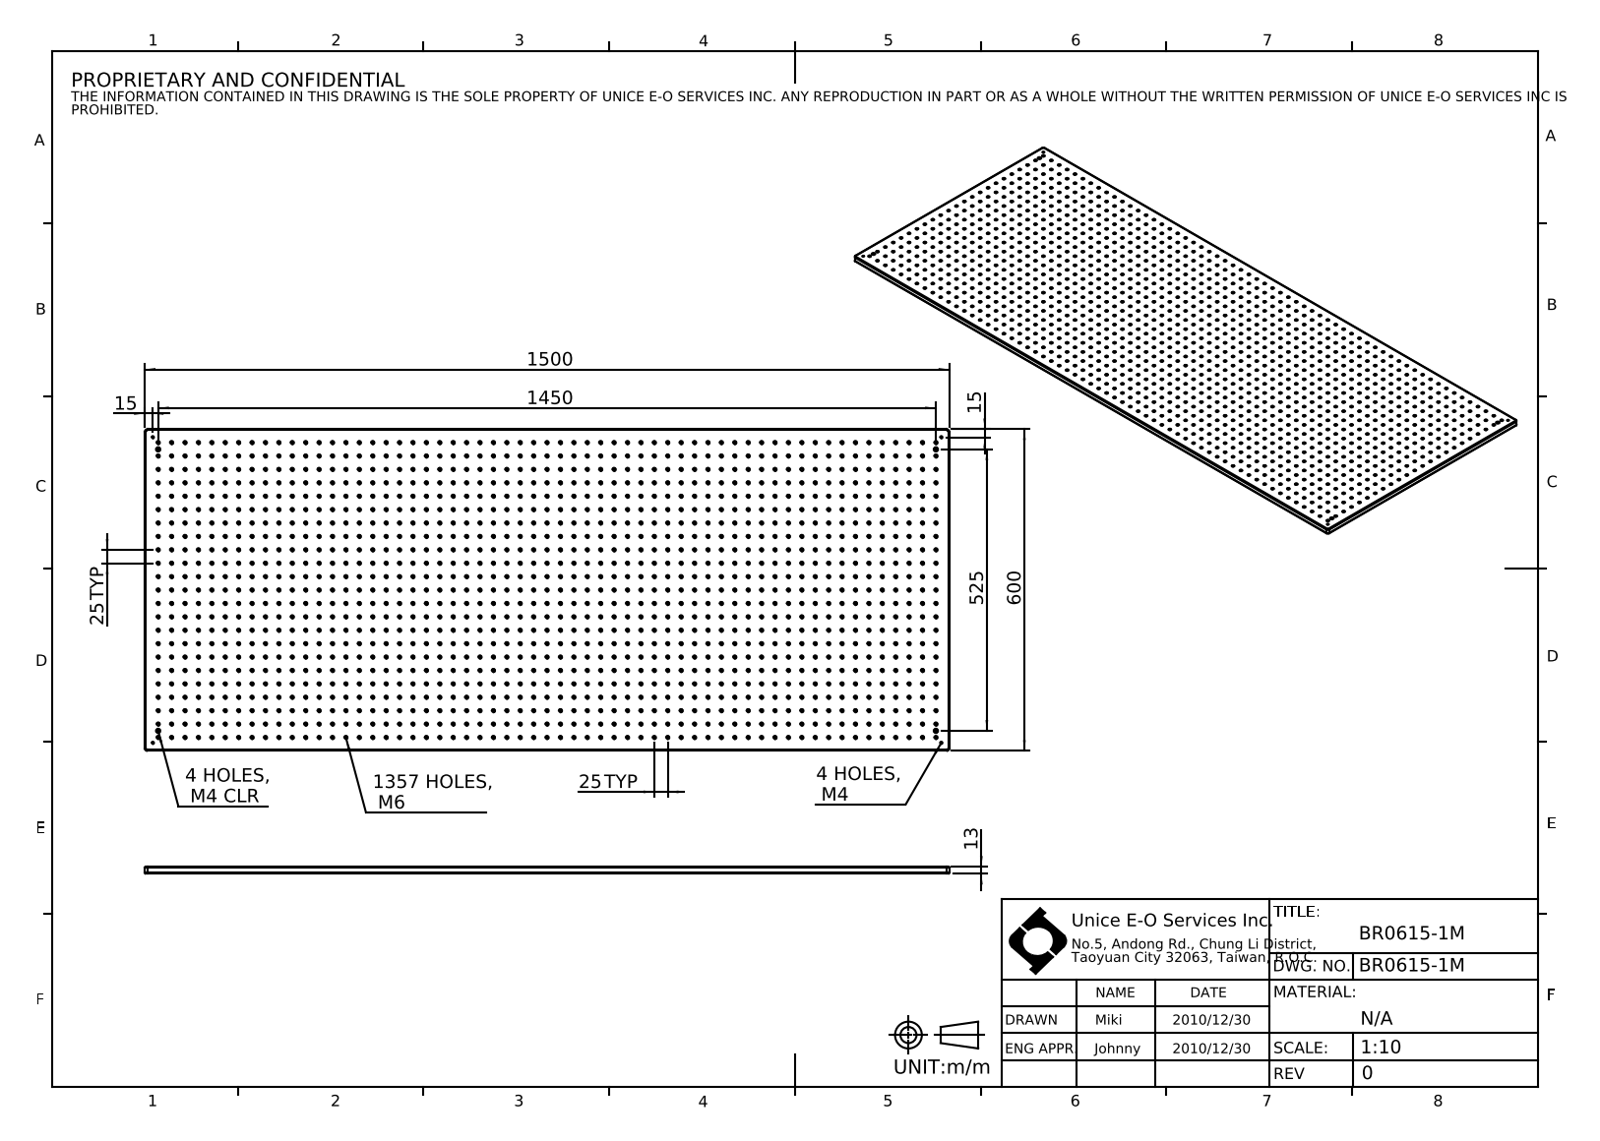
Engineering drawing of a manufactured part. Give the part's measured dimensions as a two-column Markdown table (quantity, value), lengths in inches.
| quantity | value |
| --- | --- |
| part name | BR0615-1M |
| STEP written by | SolidWorks 2016 (CONFIG_CONTROL_DESIGN) |
| units | inches |
| bodies | 1 solid, 2768 faces (10 planar, 2750 cylindrical, 8 other) |
| overall size | 59.055 × 23.622 × 0.512 |
| volume | 692 in³ |
| surface area | 3 212 in² |
| round holes (diameter × count) | 0.197 × 1357, 0.13 × 4, 0.177 × 4, 0.315 × 4 |
| partial cylindrical surfaces (radius × count) | 0.079 × 8, 0.197 × 4 |
| main face-to-face distances | 0.512, 23.622, 59.055, 0.276, 0.236 |
| hole center spacings | 0.984, 1.969, 2.953, 3.937, 4.921, 5.906, 6.89, 7.874 |
